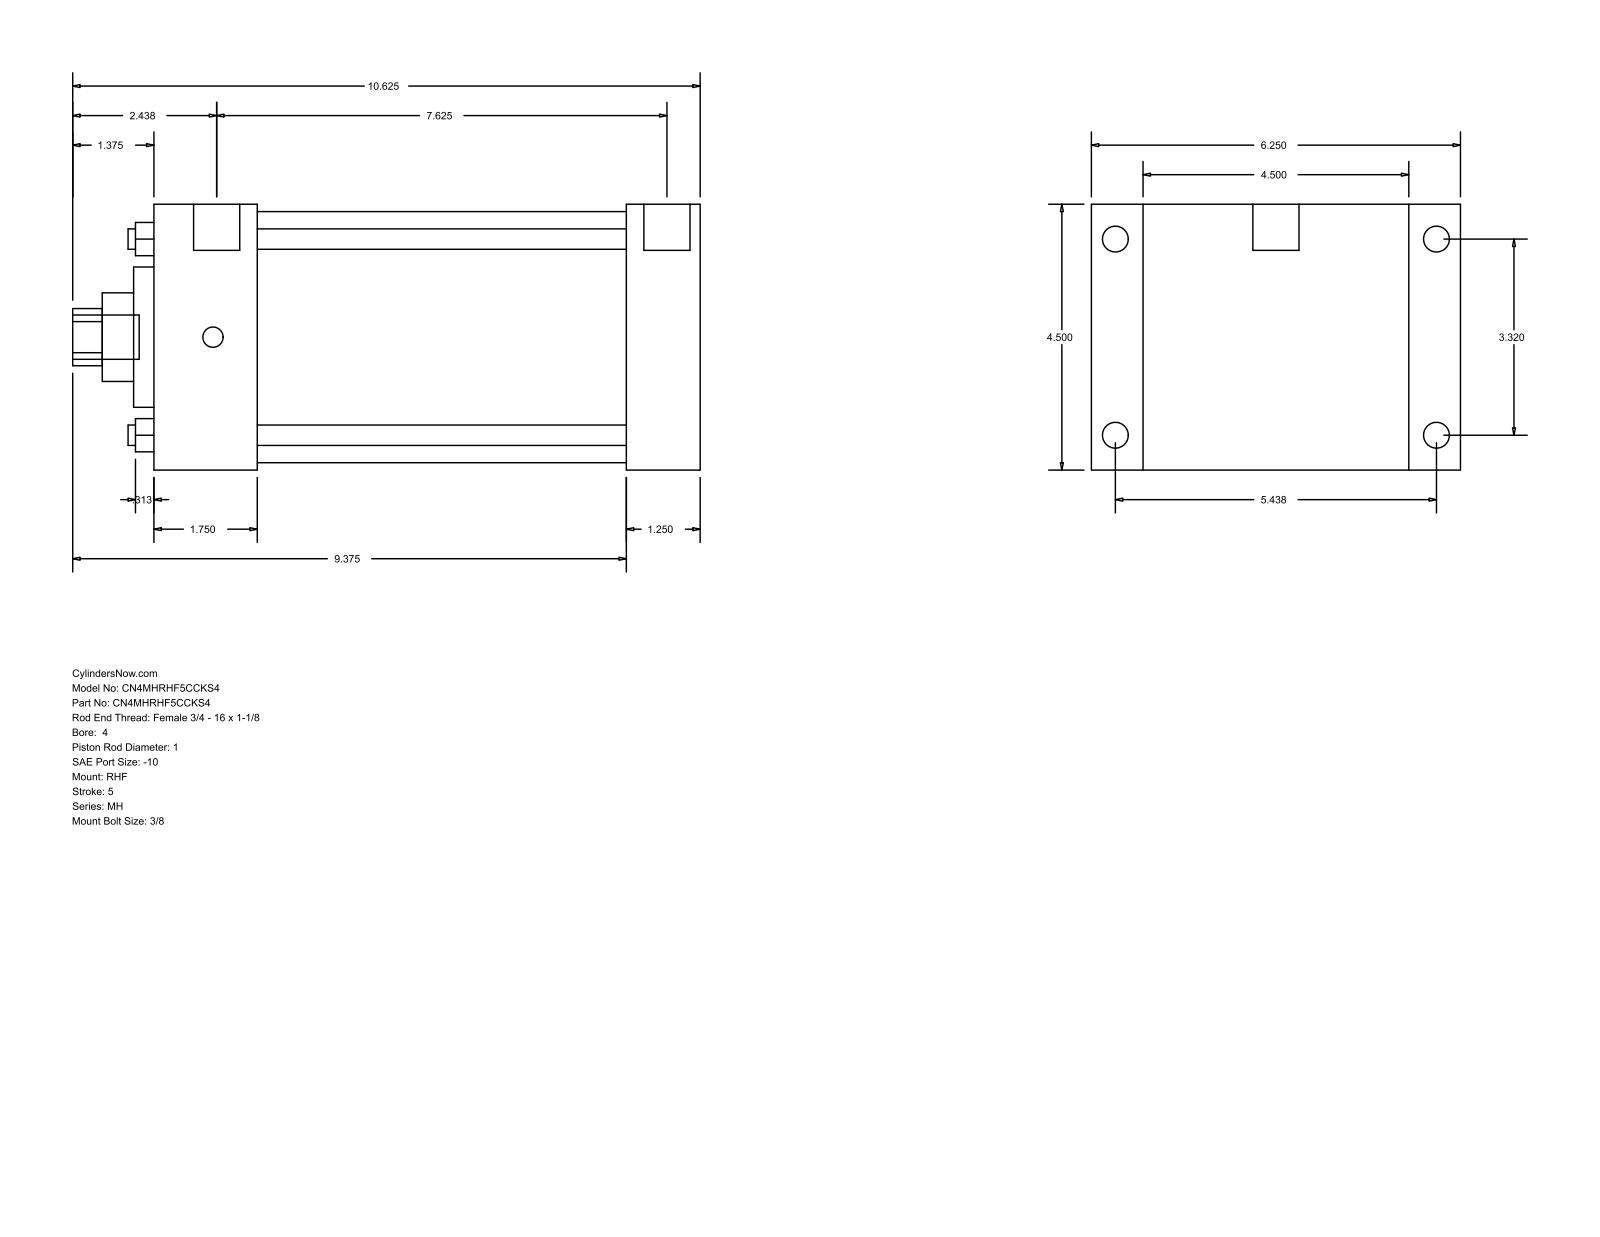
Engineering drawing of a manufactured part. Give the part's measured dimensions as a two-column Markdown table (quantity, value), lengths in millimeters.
| quantity | value |
| --- | --- |
| part name | MH_RHF__0400_1 |
| STEP written by | GSSL Pune (CONFIG_CONTROL_DESIGN) |
| units | millimeters |
| bodies | 0 solids, 90 faces (61 planar, 29 cylindrical, 0 other) |
| overall size | 269.88 × 158.75 × 114.3 |
| round holes (diameter × count) | 8.76 × 4, 25.4 × 1, 38.1 × 1, 60.33 × 1, 107.95 × 1 |
| round bosses / shafts (diameter × count) | 11.13 × 4, 8.73 × 4, 19.84 × 2, 19.05 × 1 |
| partial cylindrical surfaces (radius × count) | 12.29 × 1 |
| main face-to-face distances | 114.3, 234.96, 203.2, 31.76, 22.23, 136.53, 44.46, 158.74, 190.5, 158.76 |
| hole center spacings | 59.62, 84.32, 119.25 |
